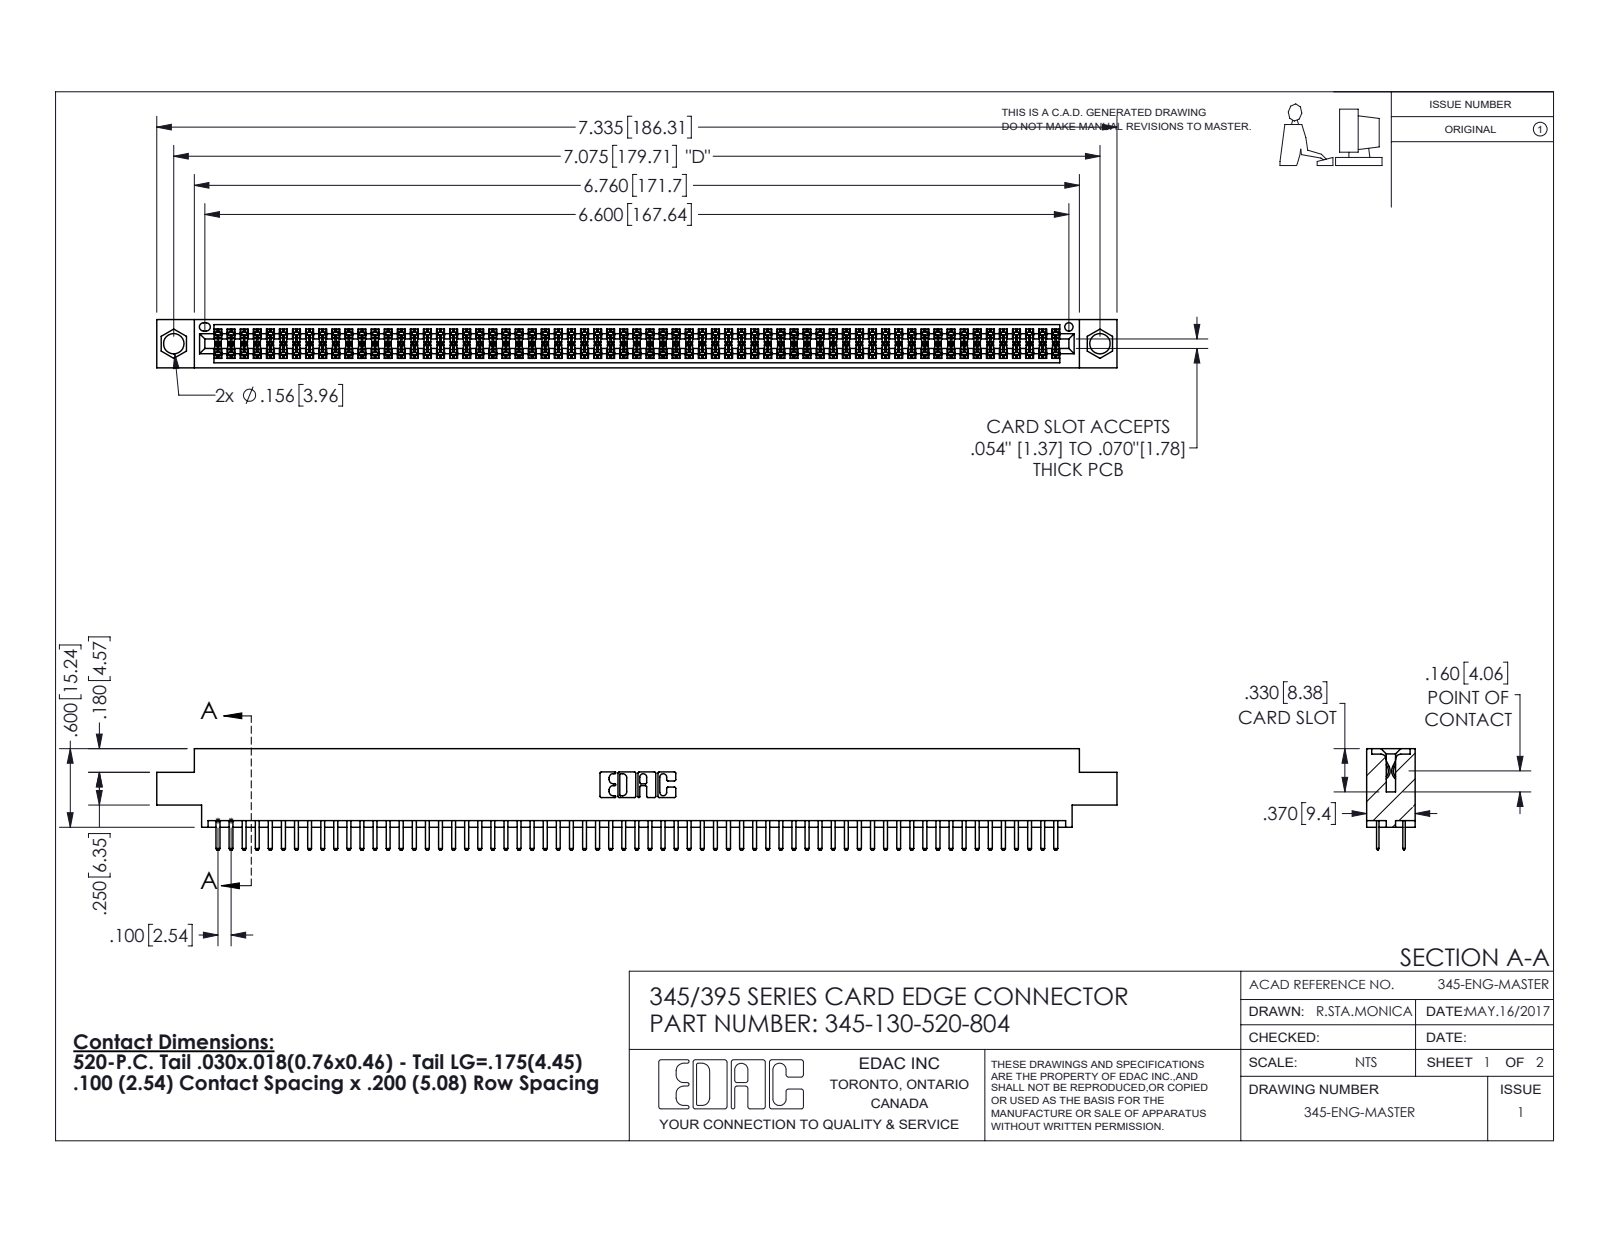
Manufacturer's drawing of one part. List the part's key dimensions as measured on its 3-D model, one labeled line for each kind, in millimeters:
Part name (STEP PRODUCT): 345 Part_0.170 Offset - 0.156 Dia-TI; 345-292-001_345-293-120; 345-130-520-804
STEP written by: SolidWorks 2020 (CONFIG_CONTROL_DESIGN)
Units: millimetres
Bodies: 131 solids, 7164 faces (4648 planar, 2516 cylindrical, 0 other)
Overall size (bounding box): 186.3 × 19.7 × 9.4
Volume: 18 040 mm³ · Surface area: 26 980 mm²
Round holes (diameter × count): ⌀4 ×2, ⌀1.6 ×1
Partial cylindrical surfaces — rounded edges, fillets, slot ends (radius × count): R0.2 ×195, R0.3 ×134, R0.3 ×22, R0.2 ×6, R0.8 ×6, R0.7 ×3, R0.4 ×2, R0.5 ×2
Main face-to-face distances: 1.8, 7.6, 5.1, 9.4, 2.5, 6.9, 0.6, 5.7, 0.6, 1.8
Hole centre spacings: 6.9, 173.7, 179.7
